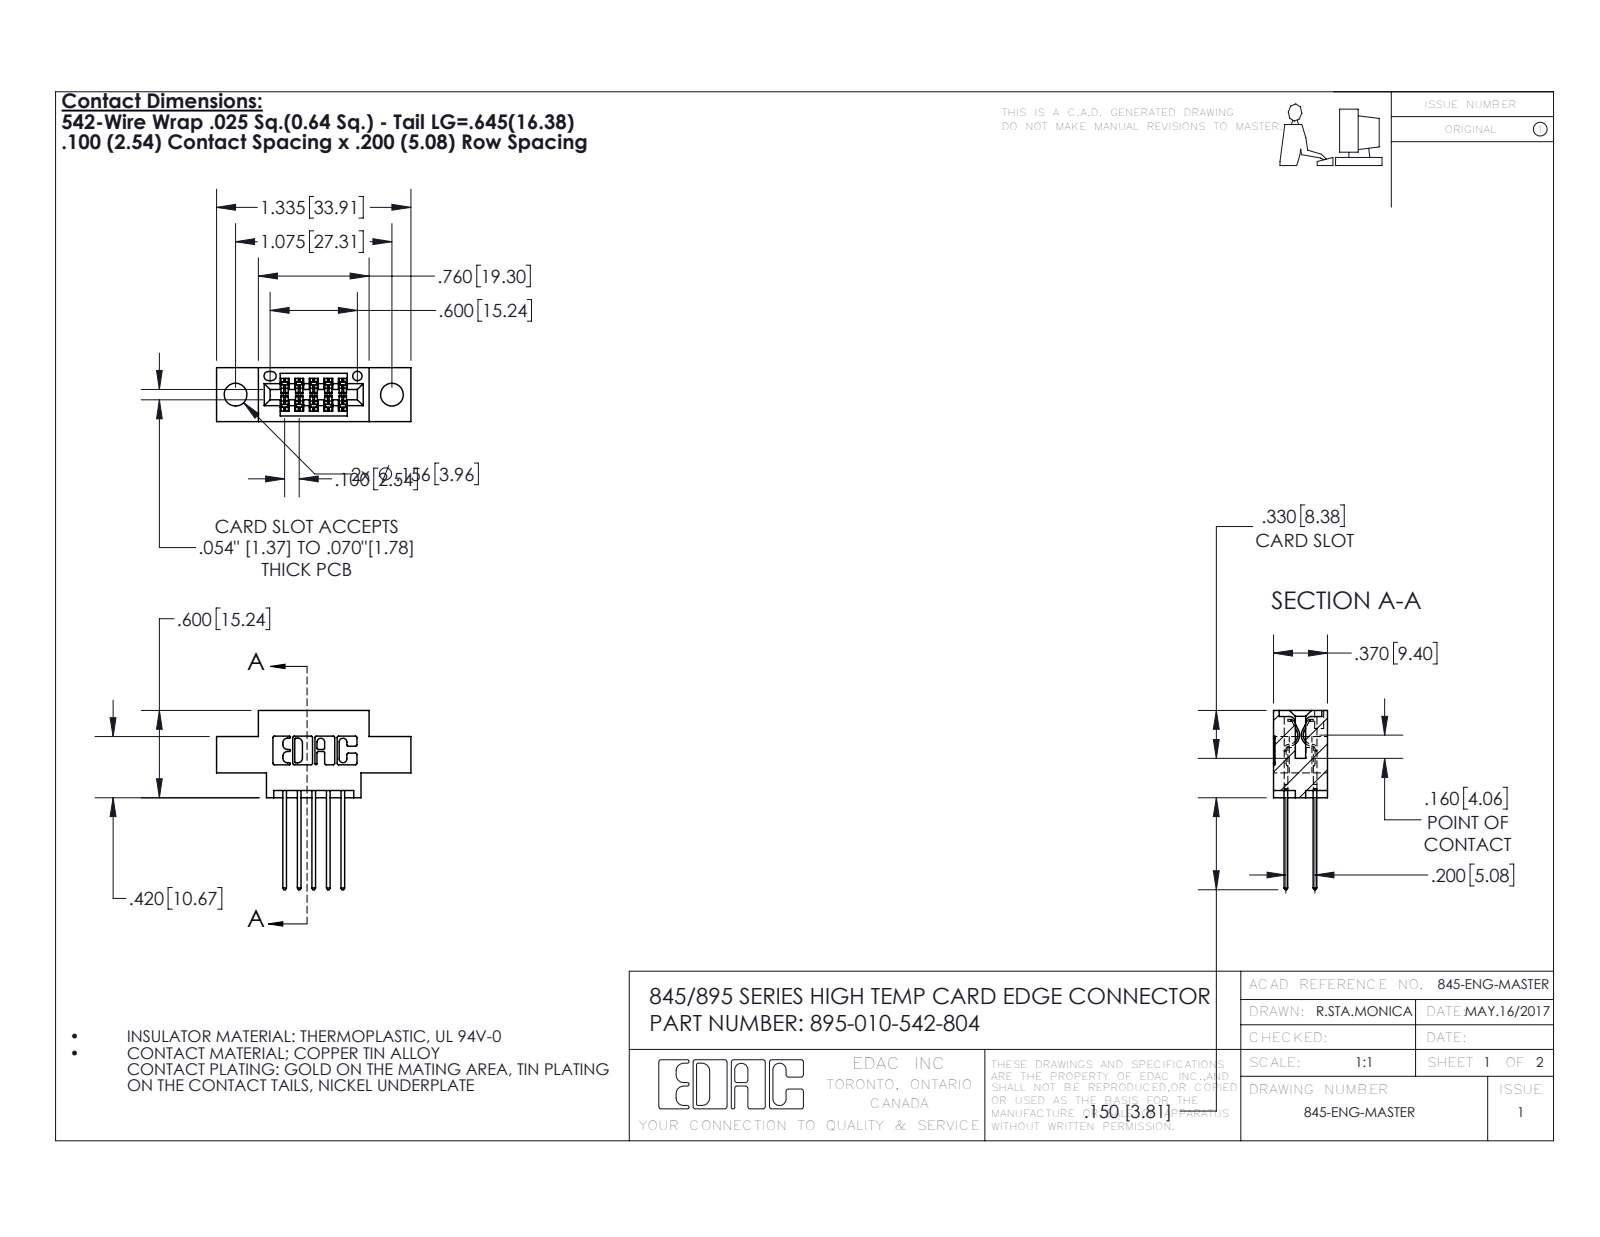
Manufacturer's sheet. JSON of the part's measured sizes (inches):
{"part_name": "395-010-542-804; 345-292-001_345-293-142; 345 Part_0.170 Offset - 0.156 Dia-TH", "step_written_by": "SolidWorks 2016 (CONFIG_CONTROL_DESIGN)", "units": "inches", "bodies": {"solids": 11, "faces": 630, "planar": 414, "cylindrical": 216, "other": 0}, "overall_size": [1.335, 1.232, 0.37], "volume_in3": 0.171, "surface_area_in2": 5.569, "round_holes": [[0.156, 2], [0.064, 1]], "partial_cylinders_radius": [[0.01, 22], [0.006, 15], [0.01, 10], [0.007, 6], [0.031, 6], [0.026, 3], [0.014, 2], [0.019, 2]], "face_to_face_distances": [0.2, 0.37, 0.072, 0.298, 0.1, 0.098, 0.272, 0.025, 0.225, 0.25], "hole_center_spacings": [0.27, 0.847, 1.075]}
